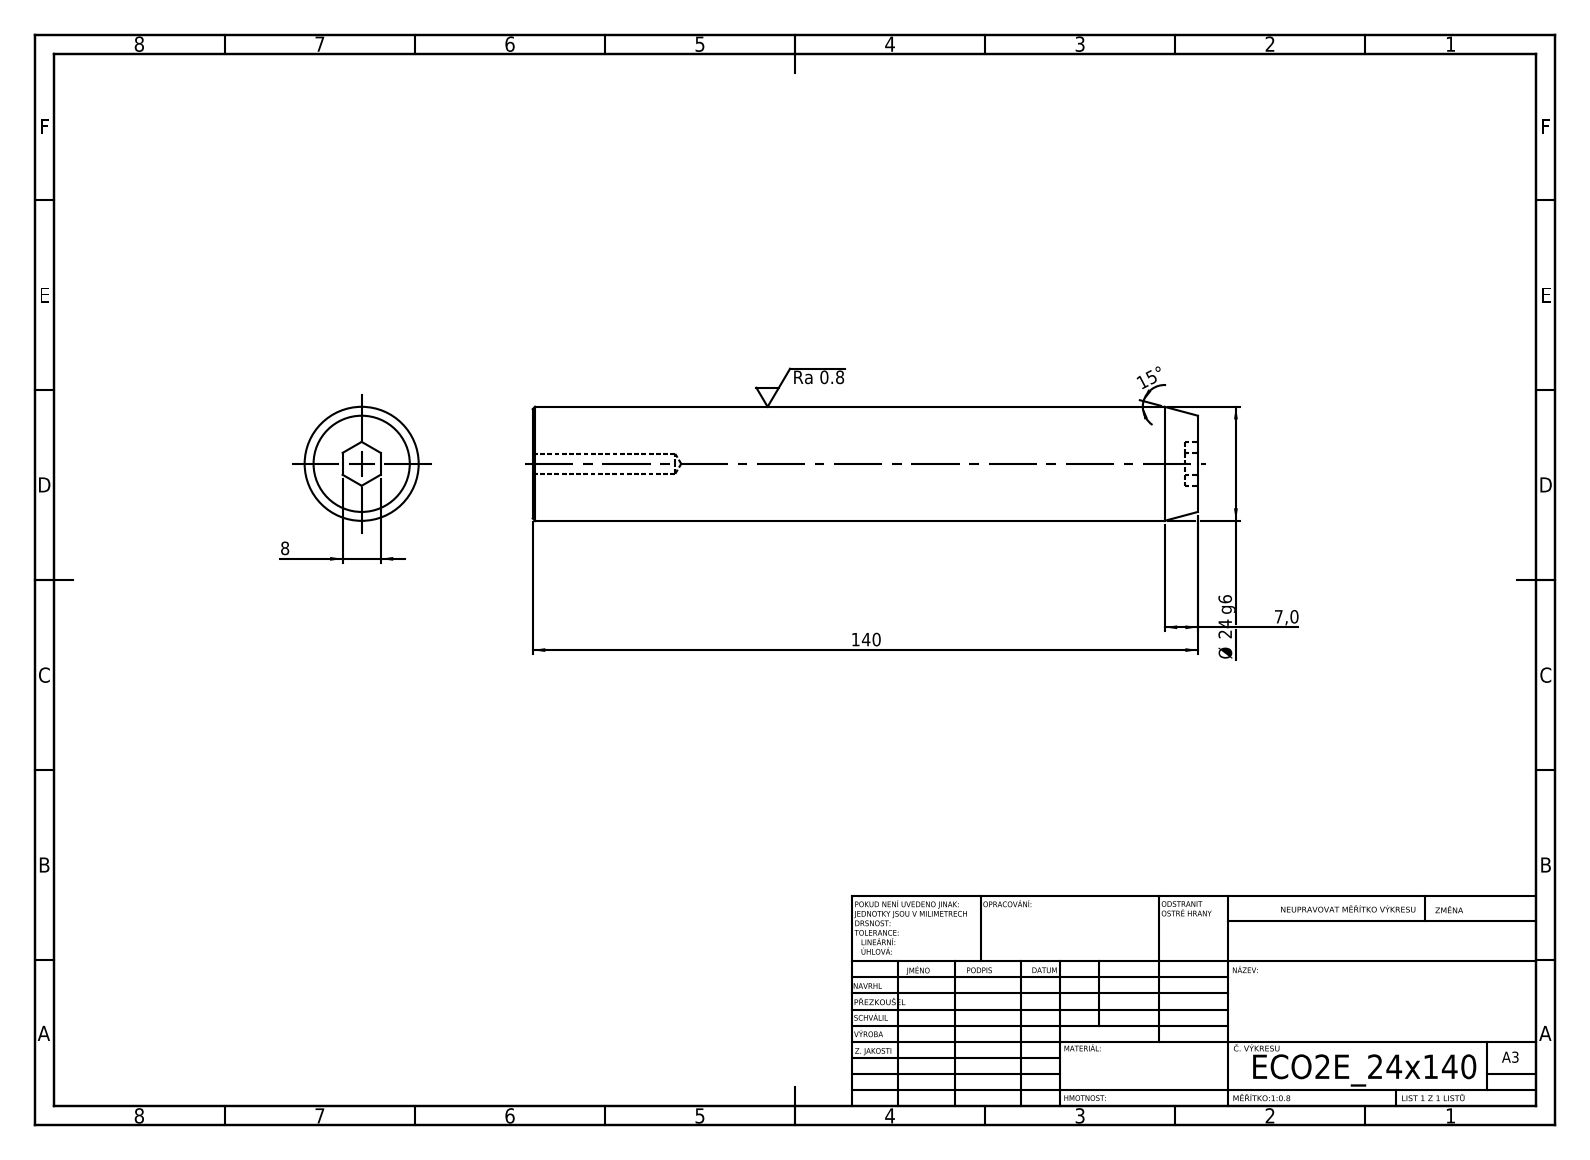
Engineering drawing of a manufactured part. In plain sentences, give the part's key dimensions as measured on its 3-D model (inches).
Its 3-D file was written by "SolidWorks 2019 (CONFIG_CONTROL_DESIGN)". It is 1 solid with 19 faces: 9 planar, 4 cylindrical and 6 other. Overall it measures 5.512 by 0.945 by 0.945 inches. Its volume is 3.8 cubic inches and its surface area 18.23 square inches. Round holes: 1 of diameter 0.165. Round bosses or shafts: 1 of diameter 0.945. The main face-to-face distances are 5.512, 0.11, 5.402, 0.315.
